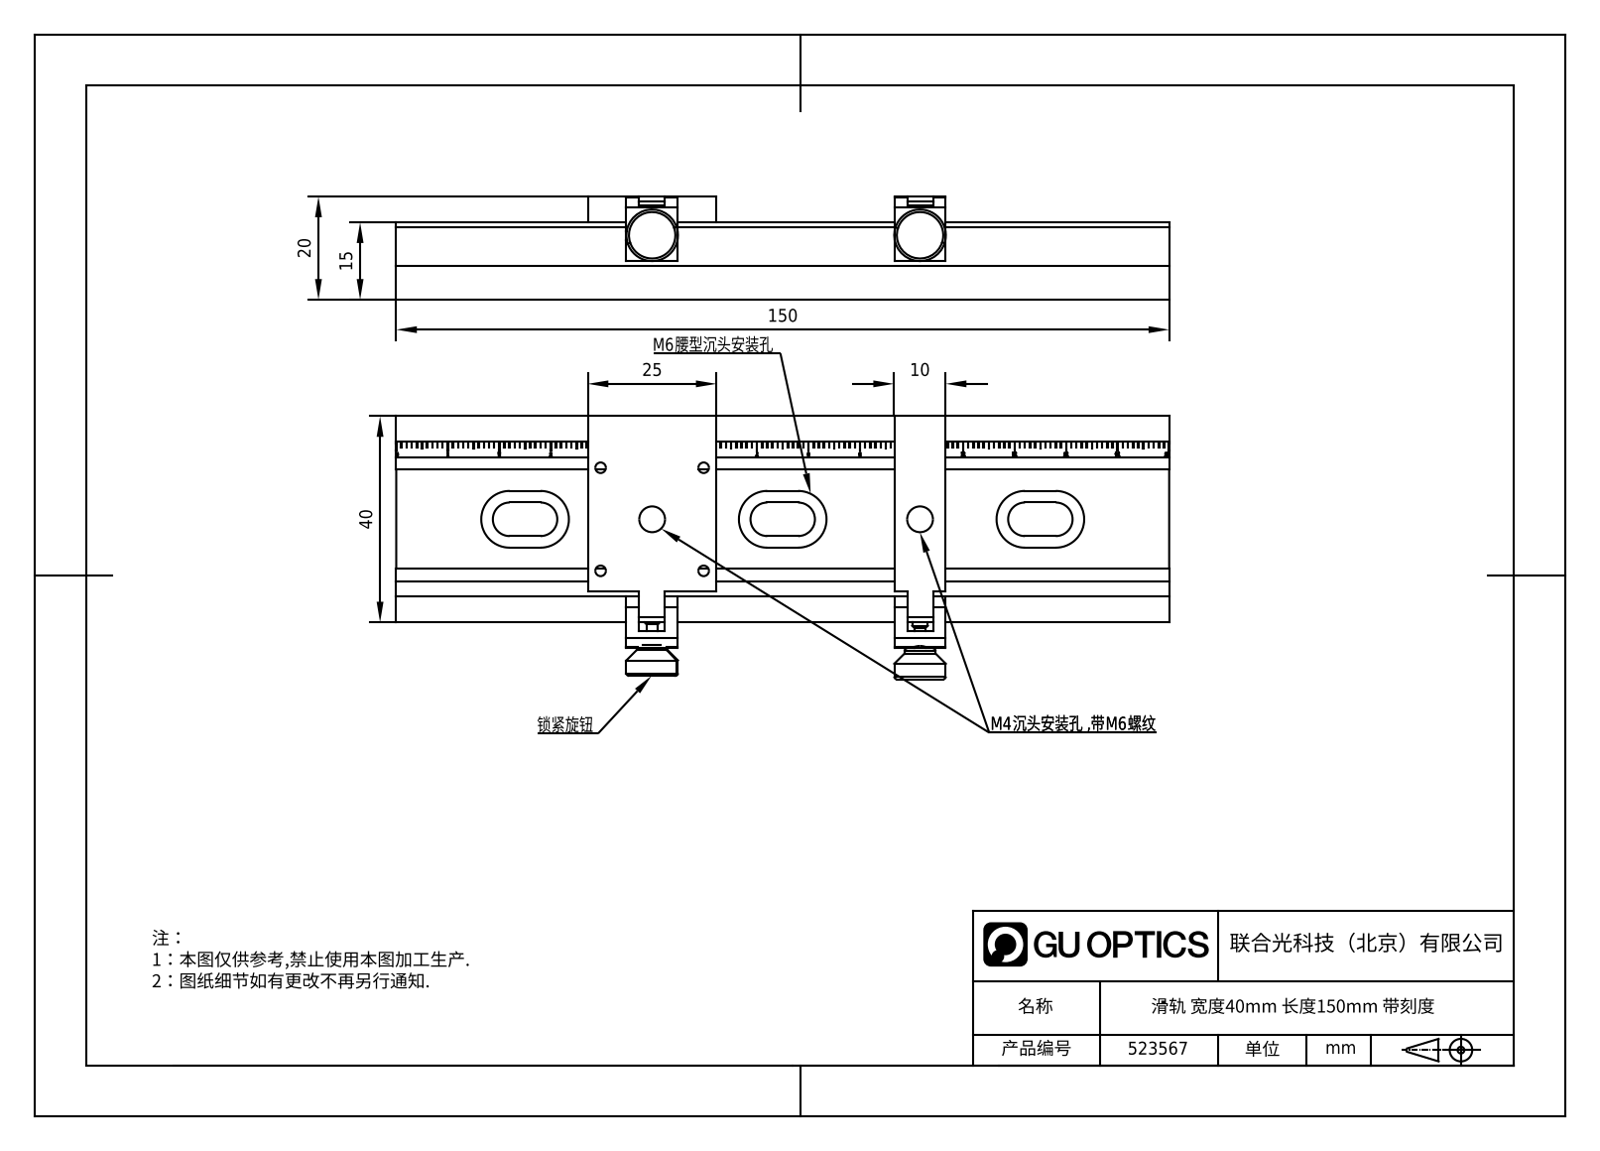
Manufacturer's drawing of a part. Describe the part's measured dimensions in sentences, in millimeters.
The part is named "523567". Its 3-D file was written by "SolidWorks 2020 (CONFIG_CONTROL_DESIGN)". It is 8 solids with 1421 faces: 1113 planar, 83 cylindrical and 225 other. Overall it measures 150 by 51.03 by 20 millimeters. Its volume is 64 253 cubic millimeters and its surface area 27 227 square millimeters. Round holes: 4 of diameter 2.05, 2 of diameter 2.5, 2 of diameter 3.2, 2 of diameter 5, 2 of diameter 8, 1 of diameter 1.5, 1 of diameter 2. Round bosses or shafts: 2 of diameter 10, 2 of diameter 6, 2 of diameter 3, 2 of diameter 2.2. Partial cylindrical surfaces (rounded edges, fillets, slot ends): 6 of radius 3.25, 6 of radius 5.5, 1 of radius 1.25, 1 of radius 2.5, 1 of radius 4.5, 1 of radius 12.5. The main face-to-face distances are 6, 14.5, 0.5, 5, 15, 8.5, 6.5, 19.5, 13.5, 20. The hole center spacings are 14.14, 20, 28.28, 43.16, 51.99, 62.79.
